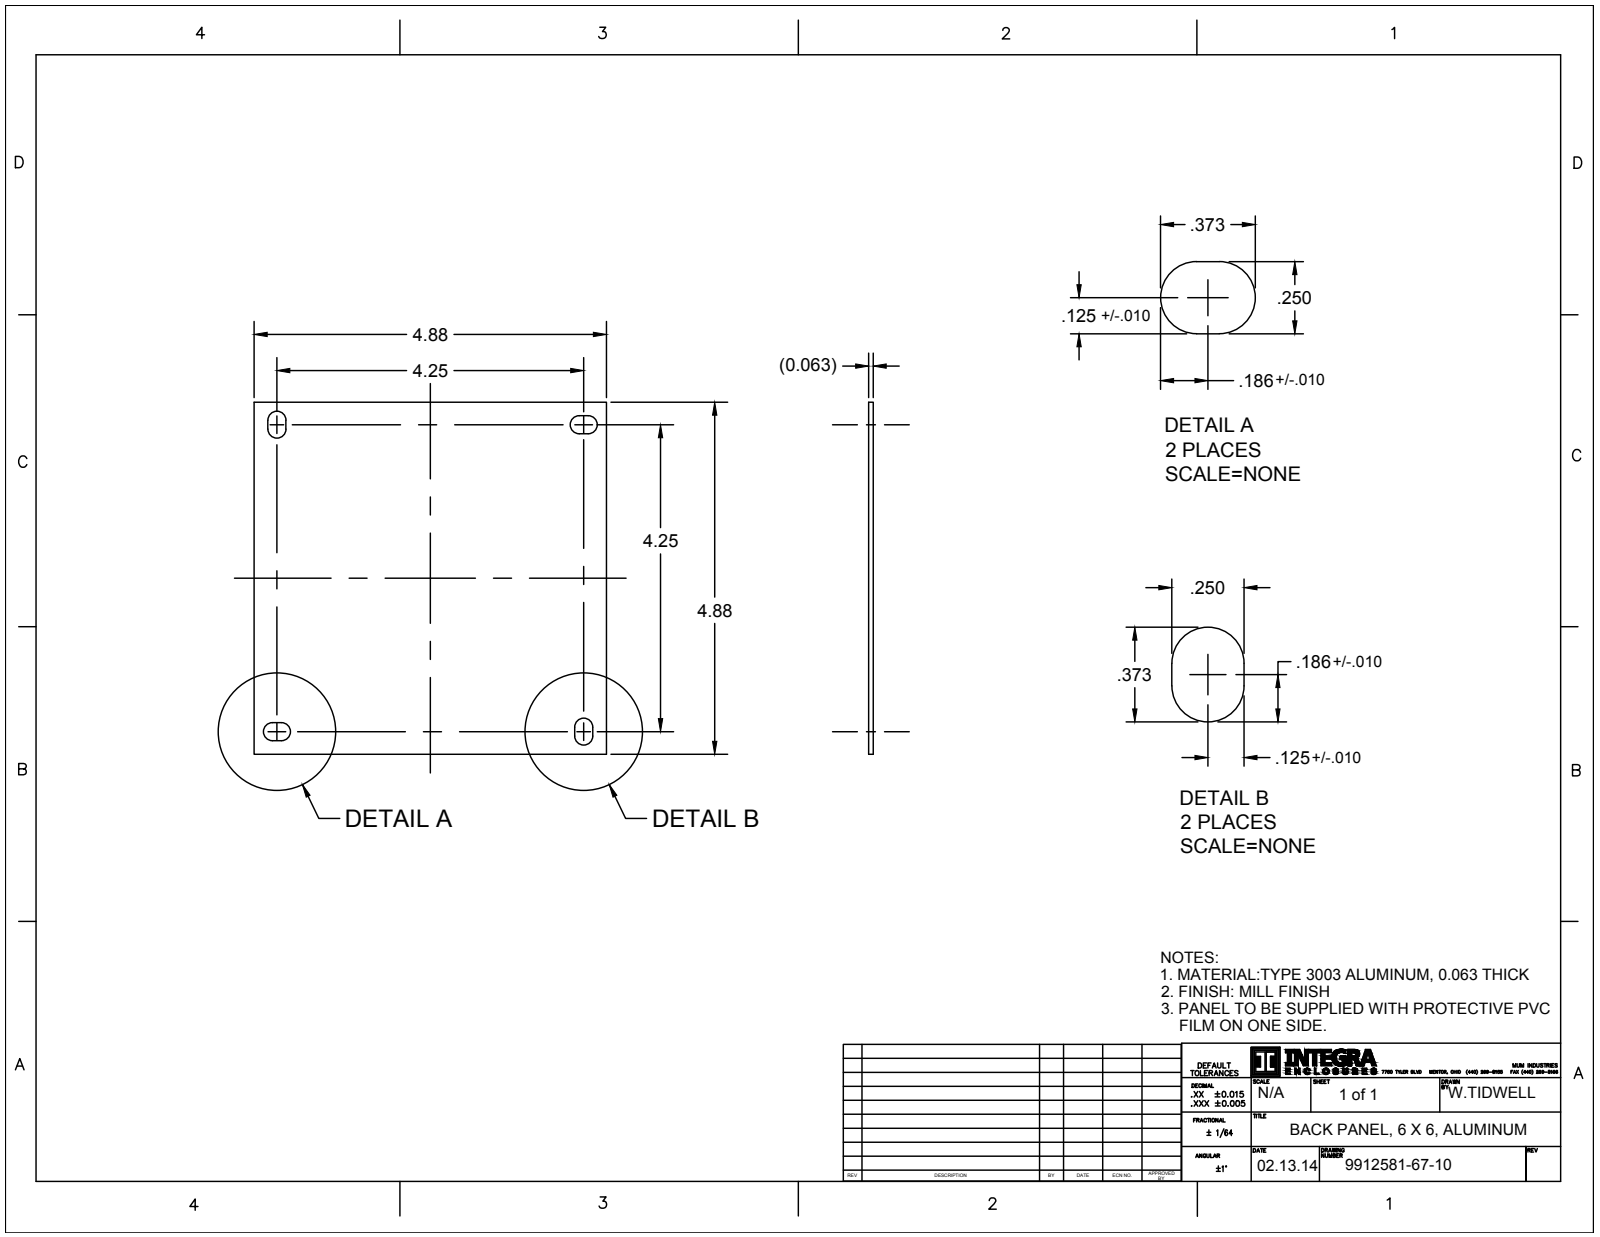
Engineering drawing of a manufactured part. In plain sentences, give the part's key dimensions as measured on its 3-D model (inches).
The part is named "9912581-67-10; 9912518-82-10; ABP66_ASM". Its 3-D file was written by "CREO PARAMETRIC BY PTC INC, 2016050 (CONFIG_CONTROL_DESIGN)". It is 5 solids with 430 faces: 90 planar, 268 cylindrical and 72 other. Overall it measures 4.88 by 4.88 by 0.443 inches. Its volume is 1.548 cubic inches and its surface area 51 square inches. Round bosses or shafts: 4 of diameter 0.373, 4 of diameter 0.19, 4 of diameter 0.149. Partial cylindrical surfaces (rounded edges, fillets, slot ends): 48 of radius 0.004, 8 of radius 0.125. The main face-to-face distances are 0.063, 4.88, 0.25, 0.313, 4.233, 0.19, 0.44, 4.44, 4.69, 0.25.
